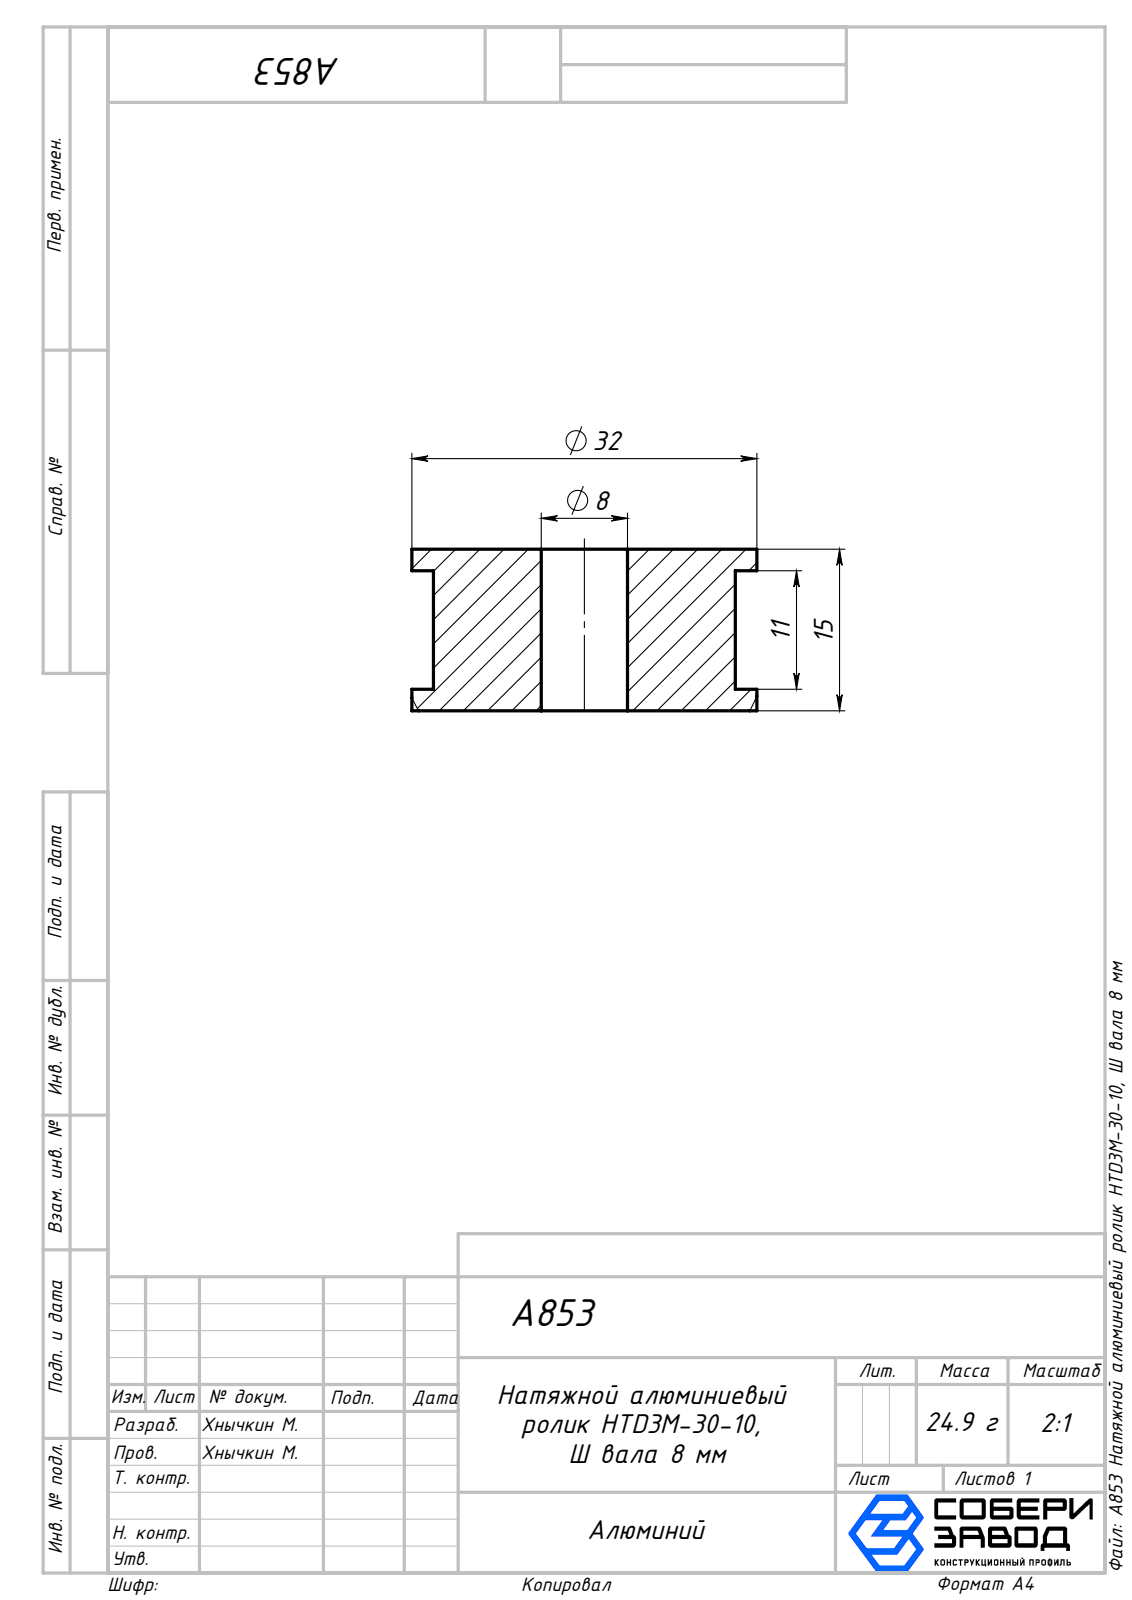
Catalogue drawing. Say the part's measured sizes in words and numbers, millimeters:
The part is named "A853 Натяжной алюминиевый ролик HTD3M-30-10, Ø вала 8 мм". Its 3-D file was written by "SolidWorks 2025 (AUTOMOTIVE_DESIGN)". It is 1 solid with 12 faces: 4 planar, 8 cylindrical and 0 other. Overall it measures 32 by 32 by 15 millimeters. Its volume is 9 236 cubic millimeters and its surface area 3 632 square millimeters. Round holes: 1 of diameter 8. Round bosses or shafts: 1 of diameter 32, 1 of diameter 28. The main face-to-face distances are 15, 2, 13, 11.
